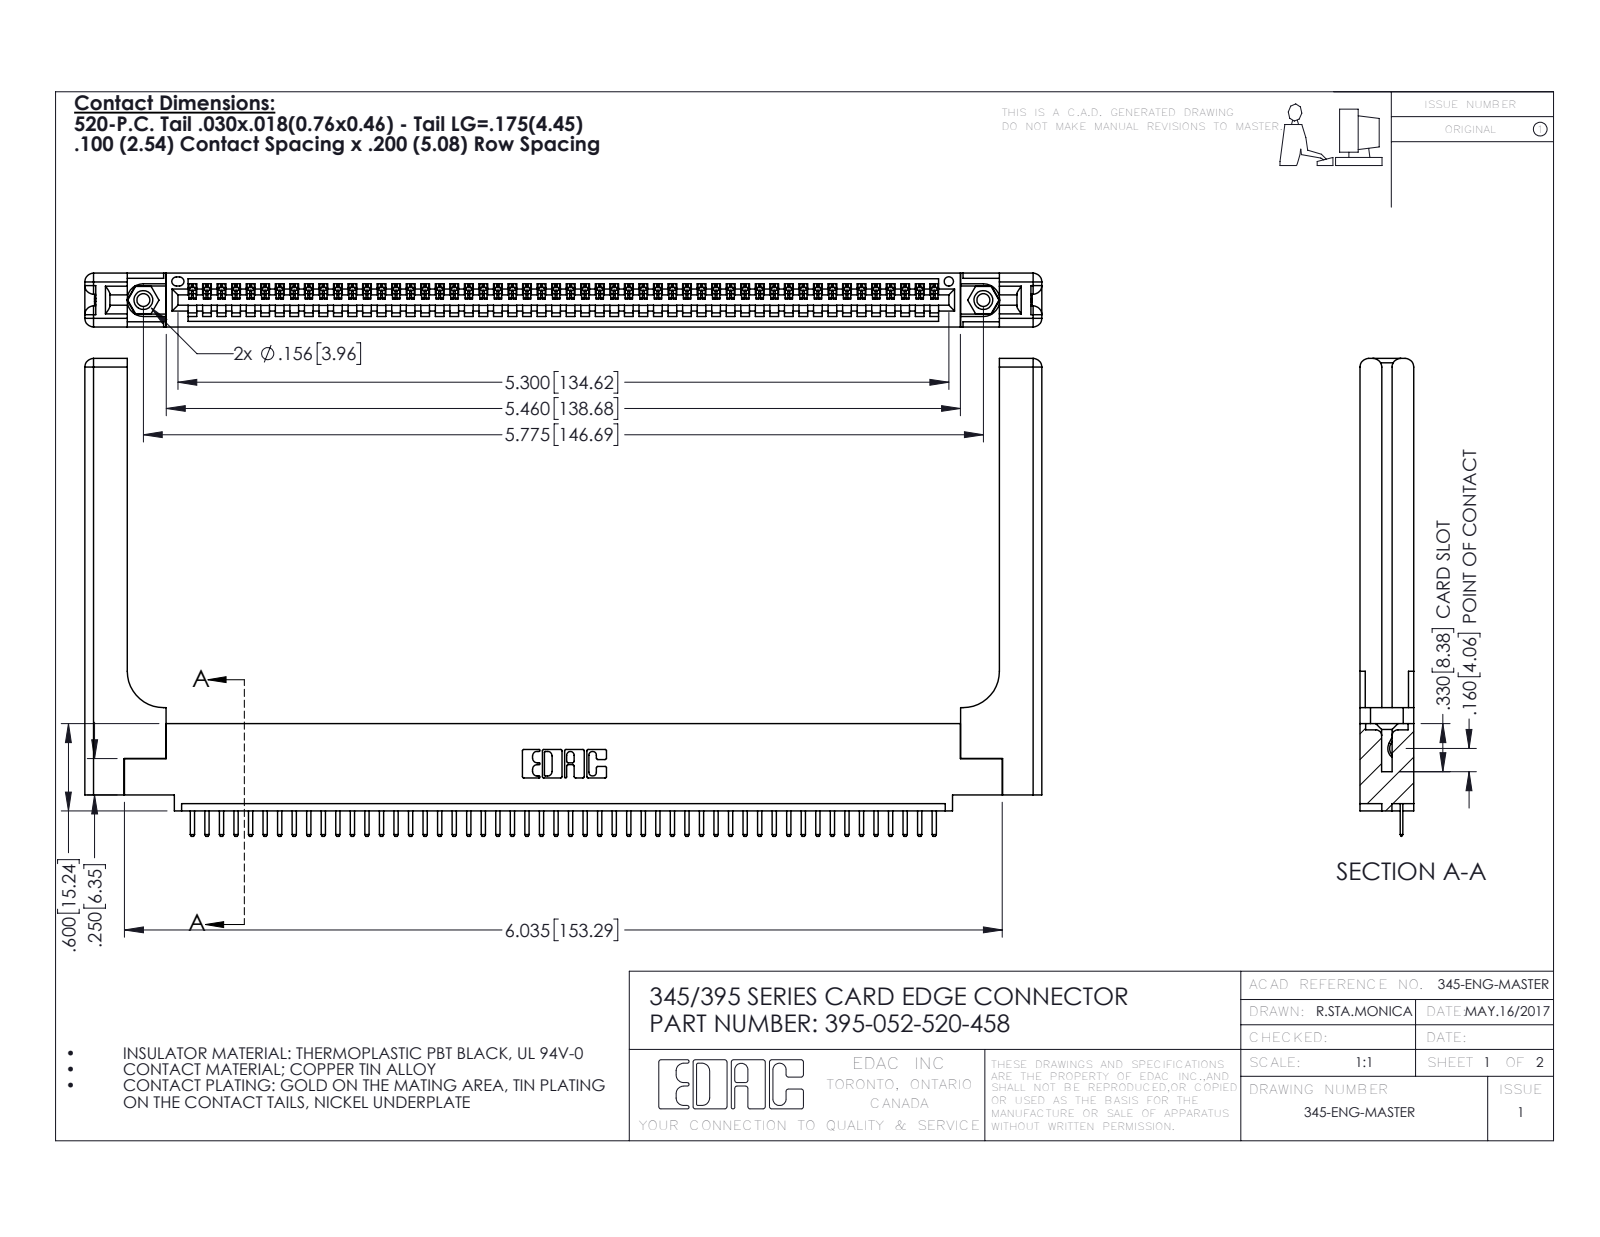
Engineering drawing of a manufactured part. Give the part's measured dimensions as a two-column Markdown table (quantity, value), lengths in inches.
| quantity | value |
| --- | --- |
| part name | 395-052-520-458; 345-250-001_345-250-001-102; 345-292-001_345-293-120; 345-220-058_345-220-058 (+1 more) |
| STEP written by | SolidWorks 2016 (CONFIG_CONTROL_DESIGN) |
| units | inches |
| bodies | 57 solids, 3610 faces (2416 planar, 1134 cylindrical, 60 other) |
| overall size | 6.579 × 3.285 × 0.37 |
| volume | 1.479 in³ |
| surface area | 40.21 in² |
| round holes (diameter × count) | 0.089 × 2, 0.125 × 2, 0.156 × 2, 0.064 × 1 |
| round bosses / shafts (diameter × count) | 0.155 × 2 |
| partial cylindrical surfaces (radius × count) | 0.01 × 106, 0.006 × 104, 0.01 × 22, 0.06 × 16, 0.007 × 6, 0.031 × 6, 0.026 × 3, 0.03 × 2 |
| main face-to-face distances | 0.37, 0.072, 0.298, 0.098, 0.272, 0.025, 0.2, 0.225, 0.148, 0.15 |
| hole center spacings | 0.27, 5.539, 5.775 |
